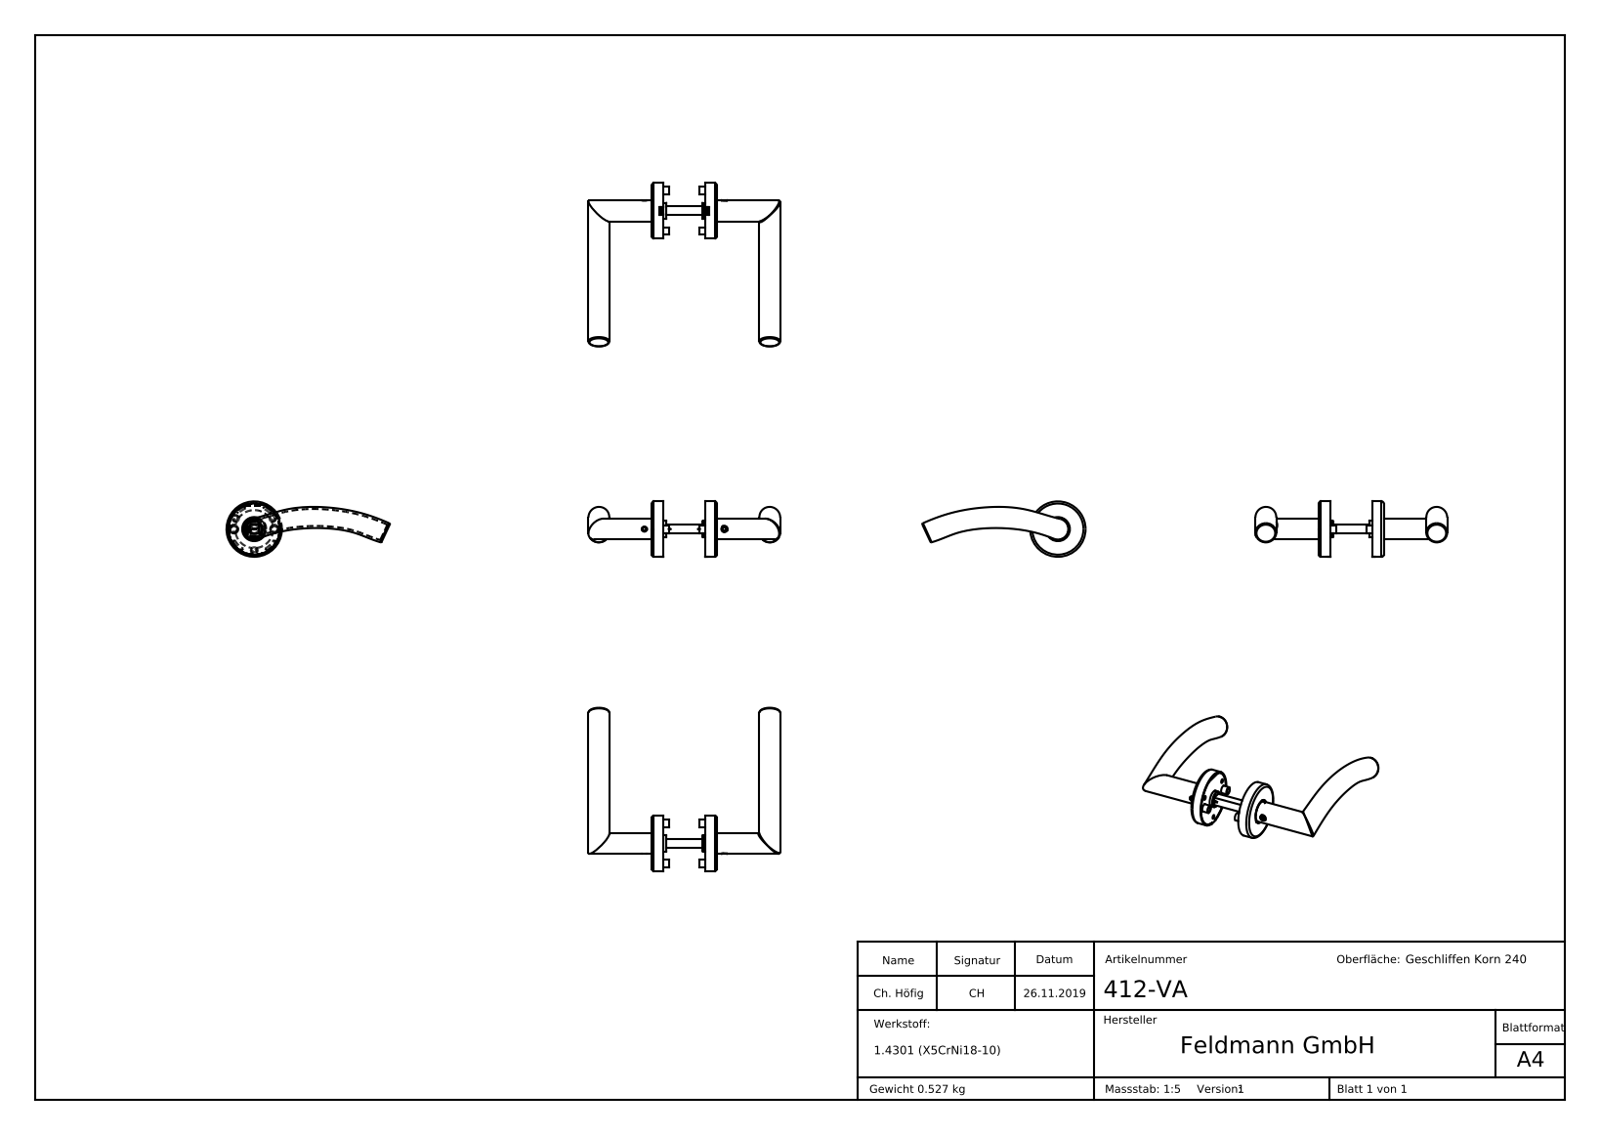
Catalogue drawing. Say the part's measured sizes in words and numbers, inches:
The part is named "412-VA; 4XX-VA Teil3; 4XX-VA Teil2; 4XX-VA Teil1 (+8 more)". Its 3-D file was written by "SolidWorks 2015 (CONFIG_CONTROL_DESIGN)". It is 15 solids with 1092 faces: 642 planar, 132 cylindrical and 318 other. Overall it measures 2755.906 by 236.215 by 236.209 inches. Its volume is 8.193 cubic inches and its surface area 192.6 square inches. Round holes: 3 of diameter 0.146, 3 of diameter 0.197, 3 of diameter 0.24, 2 of diameter 0.217, 2 of diameter 0.287, 2 of diameter 0.315, 1 of diameter 0.606, 1 of diameter 0.618, 1 of diameter 0.638, 1 of diameter 0.89. Round bosses or shafts: 2 of diameter 0.28, 2 of diameter 0.236, 1 of diameter 2.047, 1 of diameter 1.969, 1 of diameter 1.961, 1 of diameter 0.843, 1 of diameter 0.772, 1 of diameter 0.598. Partial cylindrical surfaces (rounded edges, fillets, slot ends): 4 of radius 0.039, 1 of radius 0.177, 1 of radius 0.703, 1 of radius 0.827, 1 of radius 0.906. The main face-to-face distances are 0.039, 2.362, 0.413, 1.988, 0.374, 1.949, 0.319, 1.575, 0.031, 0.315. The hole center spacings are 0.787, 1.364, 0.399, 0.748, 1.086, 1.483, 1.181, 1.496.
